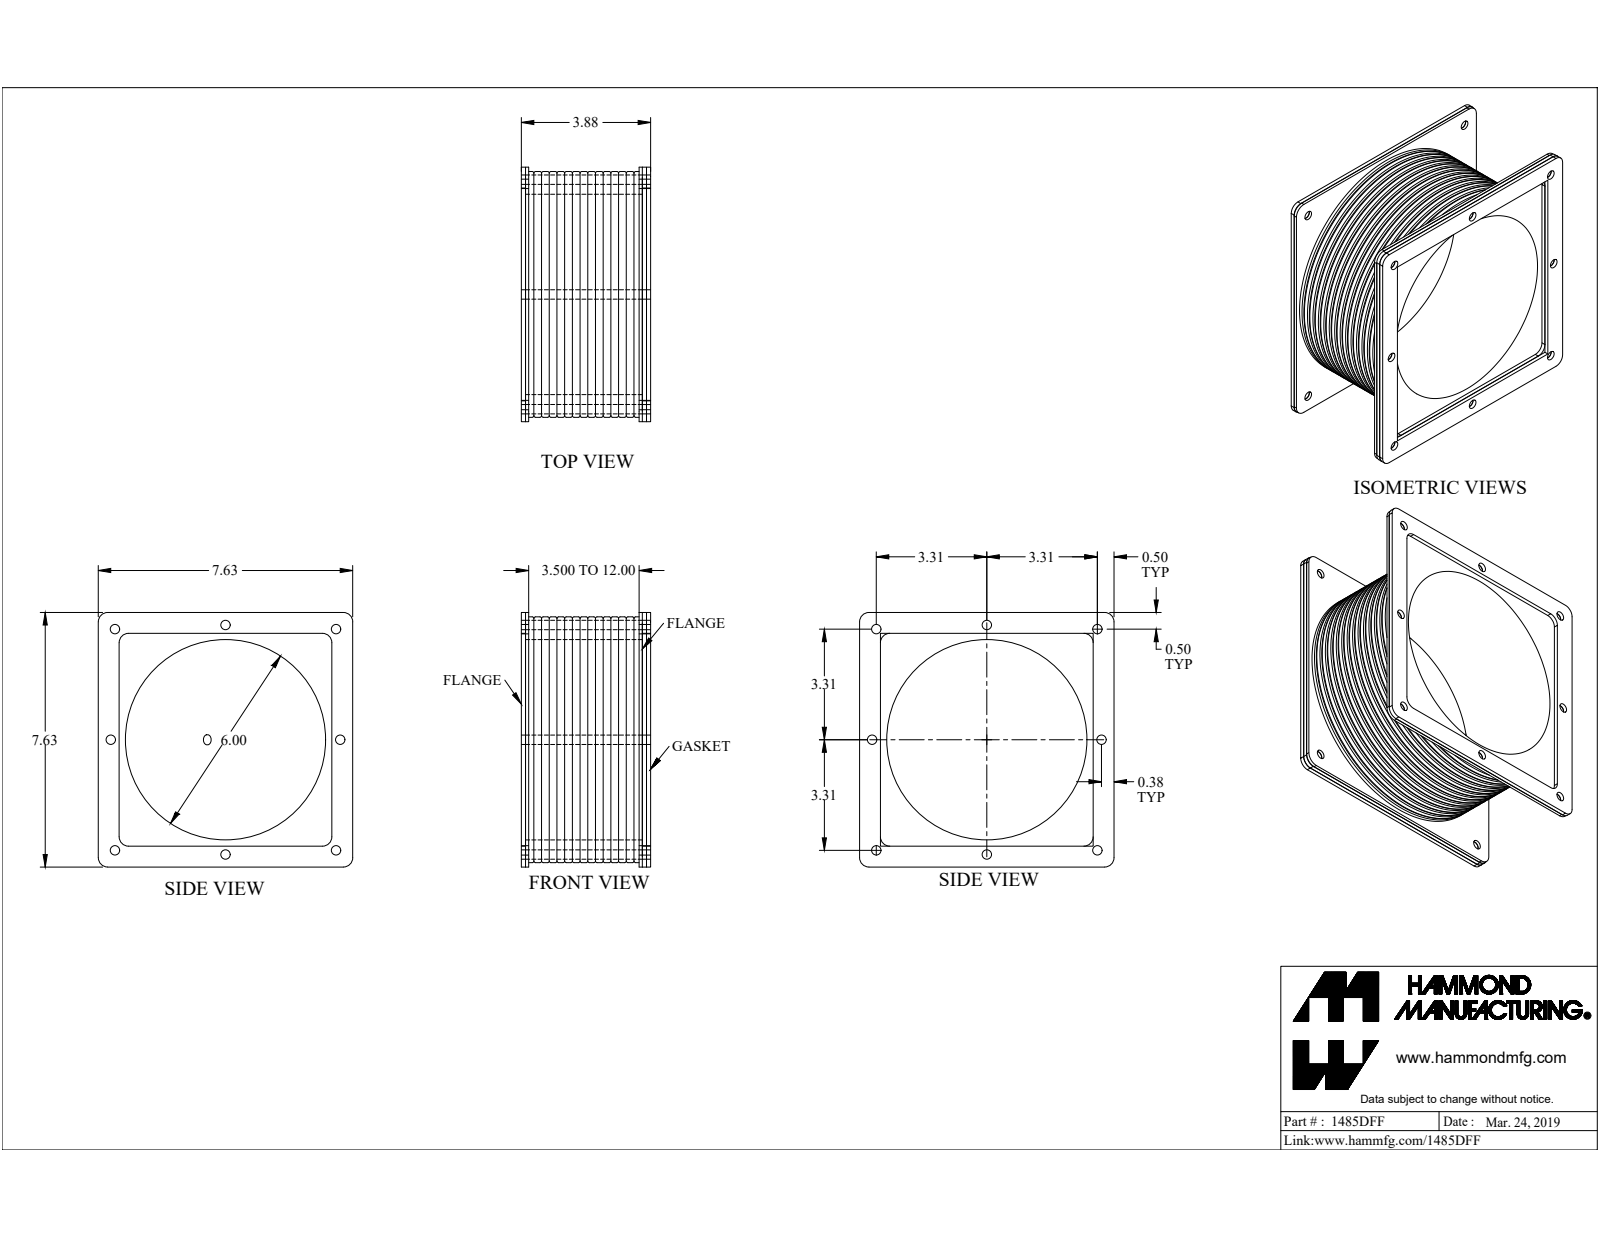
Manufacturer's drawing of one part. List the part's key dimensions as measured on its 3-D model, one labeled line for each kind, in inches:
Part name (STEP PRODUCT): 1485DFF
STEP written by: SolidWorks 2019 (CONFIG_CONTROL_DESIGN)
Units: inches
Bodies: 4 solids, 150 faces (42 planar, 80 cylindrical, 28 other)
Overall size (bounding box): 7.625 × 7.625 × 3.875
Volume: 58.04 in³ · Surface area: 393.7 in²
Round holes (diameter × count): ⌀0.281 ×8, ⌀0.281 ×8, ⌀6 ×1
Round bosses / shafts (diameter × count): ⌀7.362 ×1
Partial cylindrical surfaces — rounded edges, fillets, slot ends (radius × count): R0.281 ×8, R0.313 ×4
Main face-to-face distances: 0.125, 3.625, 3.5, 0.22, 3.53, 0.095, 3.405, 3.75, 3.875, 3.75
Hole centre spacings: 3.315, 7.519, 3.437, 4.685, 4.861, 6.625, 6.875, 9.369
